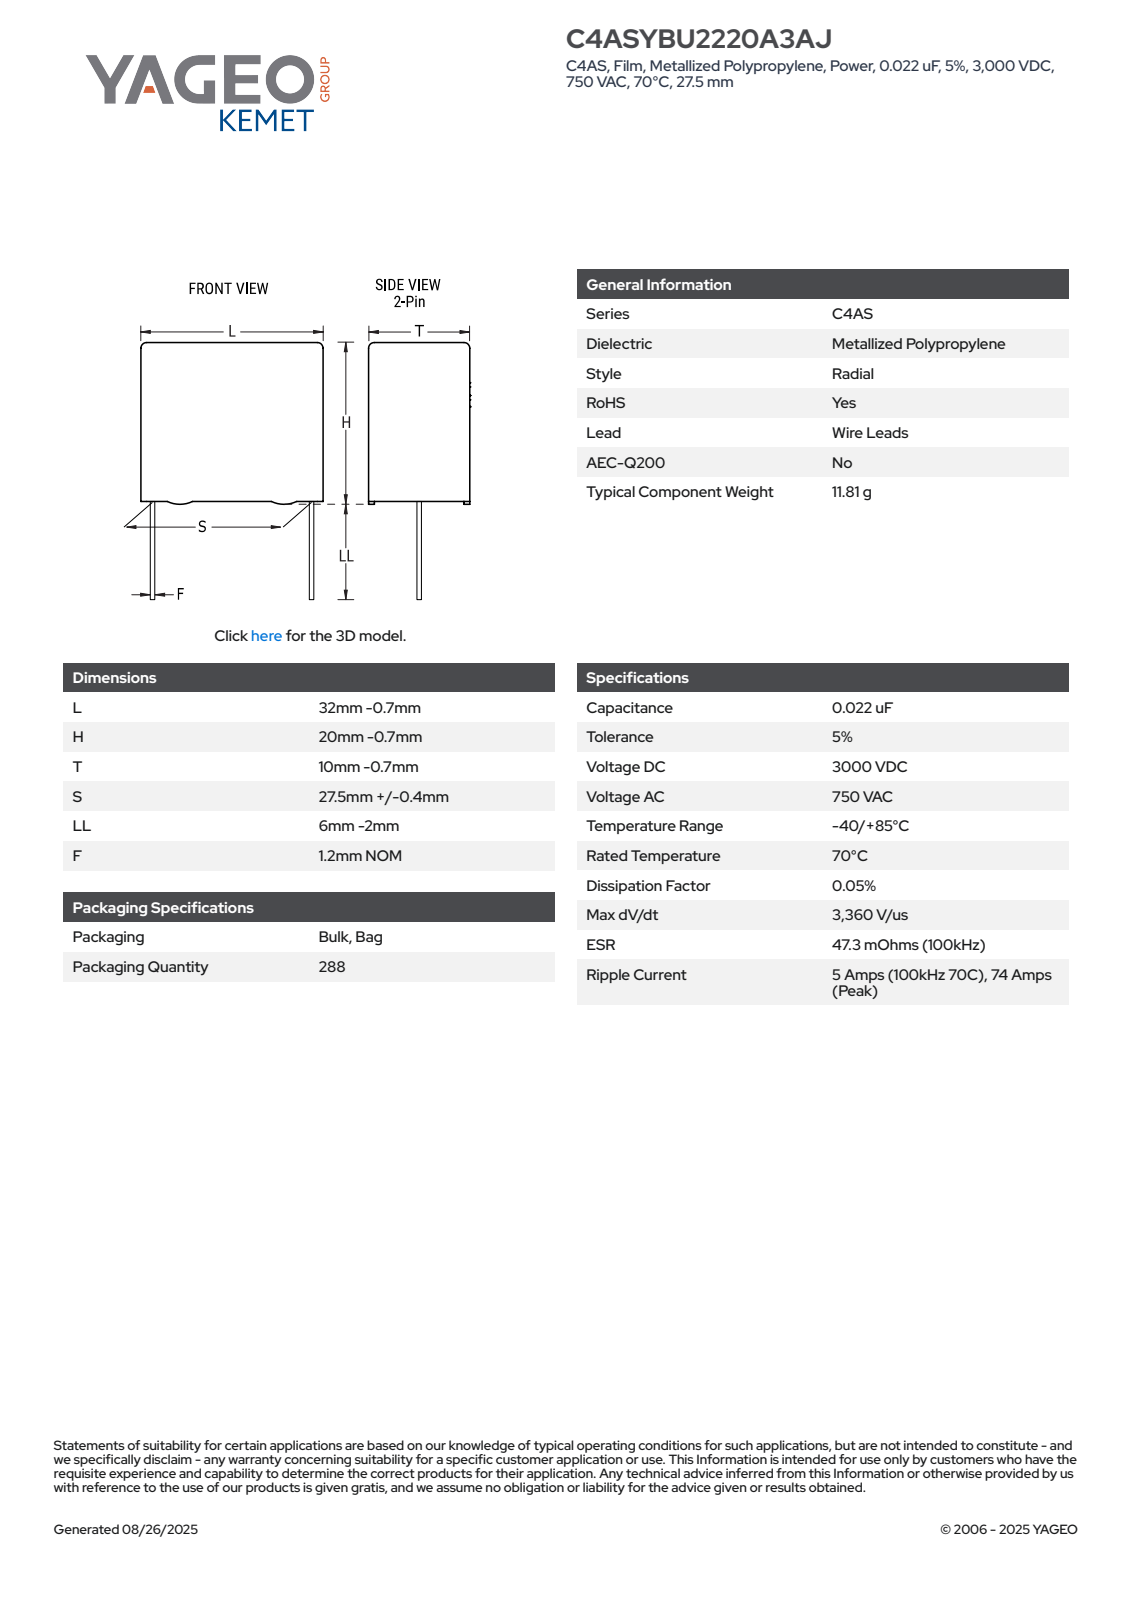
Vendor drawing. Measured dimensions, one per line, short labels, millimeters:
name: CFP_RB_32X20X10_L31.3H19.3T9.3S27.5LL4F1.2
written by: SolidWorks 2014 (AUTOMOTIVE_DESIGN)
unit: mm
bodies: 4 solids, 89 faces (81 planar, 8 cylindrical, 0 other)
size: 31.3 × 23.3 × 9.3
volume: 5 515 mm³; area: 2 194 mm²
bosses: 2× ⌀1.2
rounds: 4× R0.5
face distances: 9.3, 18.91, 31.3, 9.31, 0.39, 19.3, 0.53, 8.77, 0.54, 8.24
